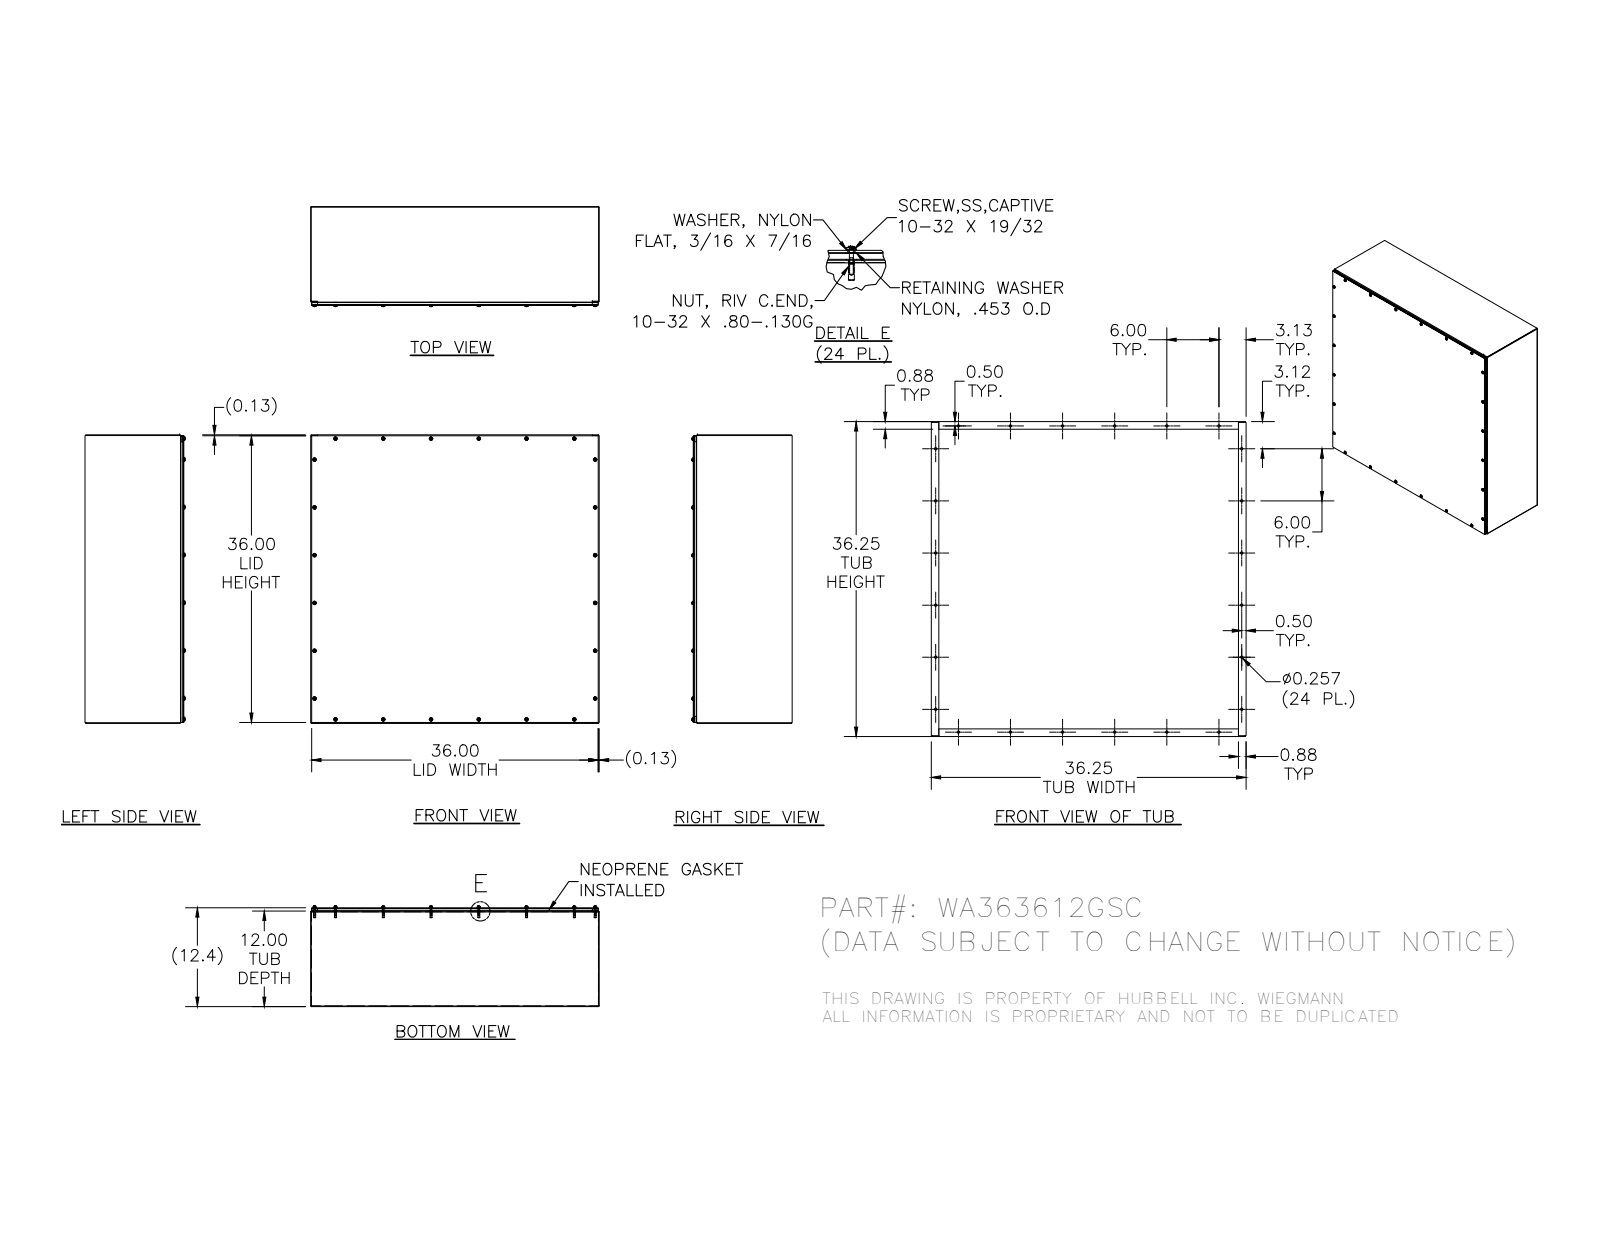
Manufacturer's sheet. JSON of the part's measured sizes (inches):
{"part_name": "37210; WA363612GSCBTM; 34984; WA3636GSCLP (+5 more)", "step_written_by": "SolidWorks 2014 (AUTOMOTIVE_DESIGN)", "units": "inches", "bodies": {"solids": 104, "faces": 2408, "planar": 1124, "cylindrical": 636, "other": 648}, "overall_size": [36.25, 36.249, 12.568], "volume_in3": 443.3, "surface_area_in2": 9256, "round_holes": [[0.156, 24], [0.188, 24], [0.196, 24], [0.257, 24], [0.278, 24], [0.281, 24]], "round_bosses_or_shafts": [[0.453, 24], [0.437, 24], [0.406, 24], [0.248, 24], [0.167, 24]], "partial_cylinders_radius": [[0.089, 24], [0.016, 6], [0.109, 6]], "face_to_face_distances": [0.094, 12.32, 12.226, 12.414, 0.094, 36.156, 36.062, 36.156, 36.25, 36.156], "hole_center_spacings": [35.757, 6, 37.237, 12, 35.25, 18, 39.58, 24]}
